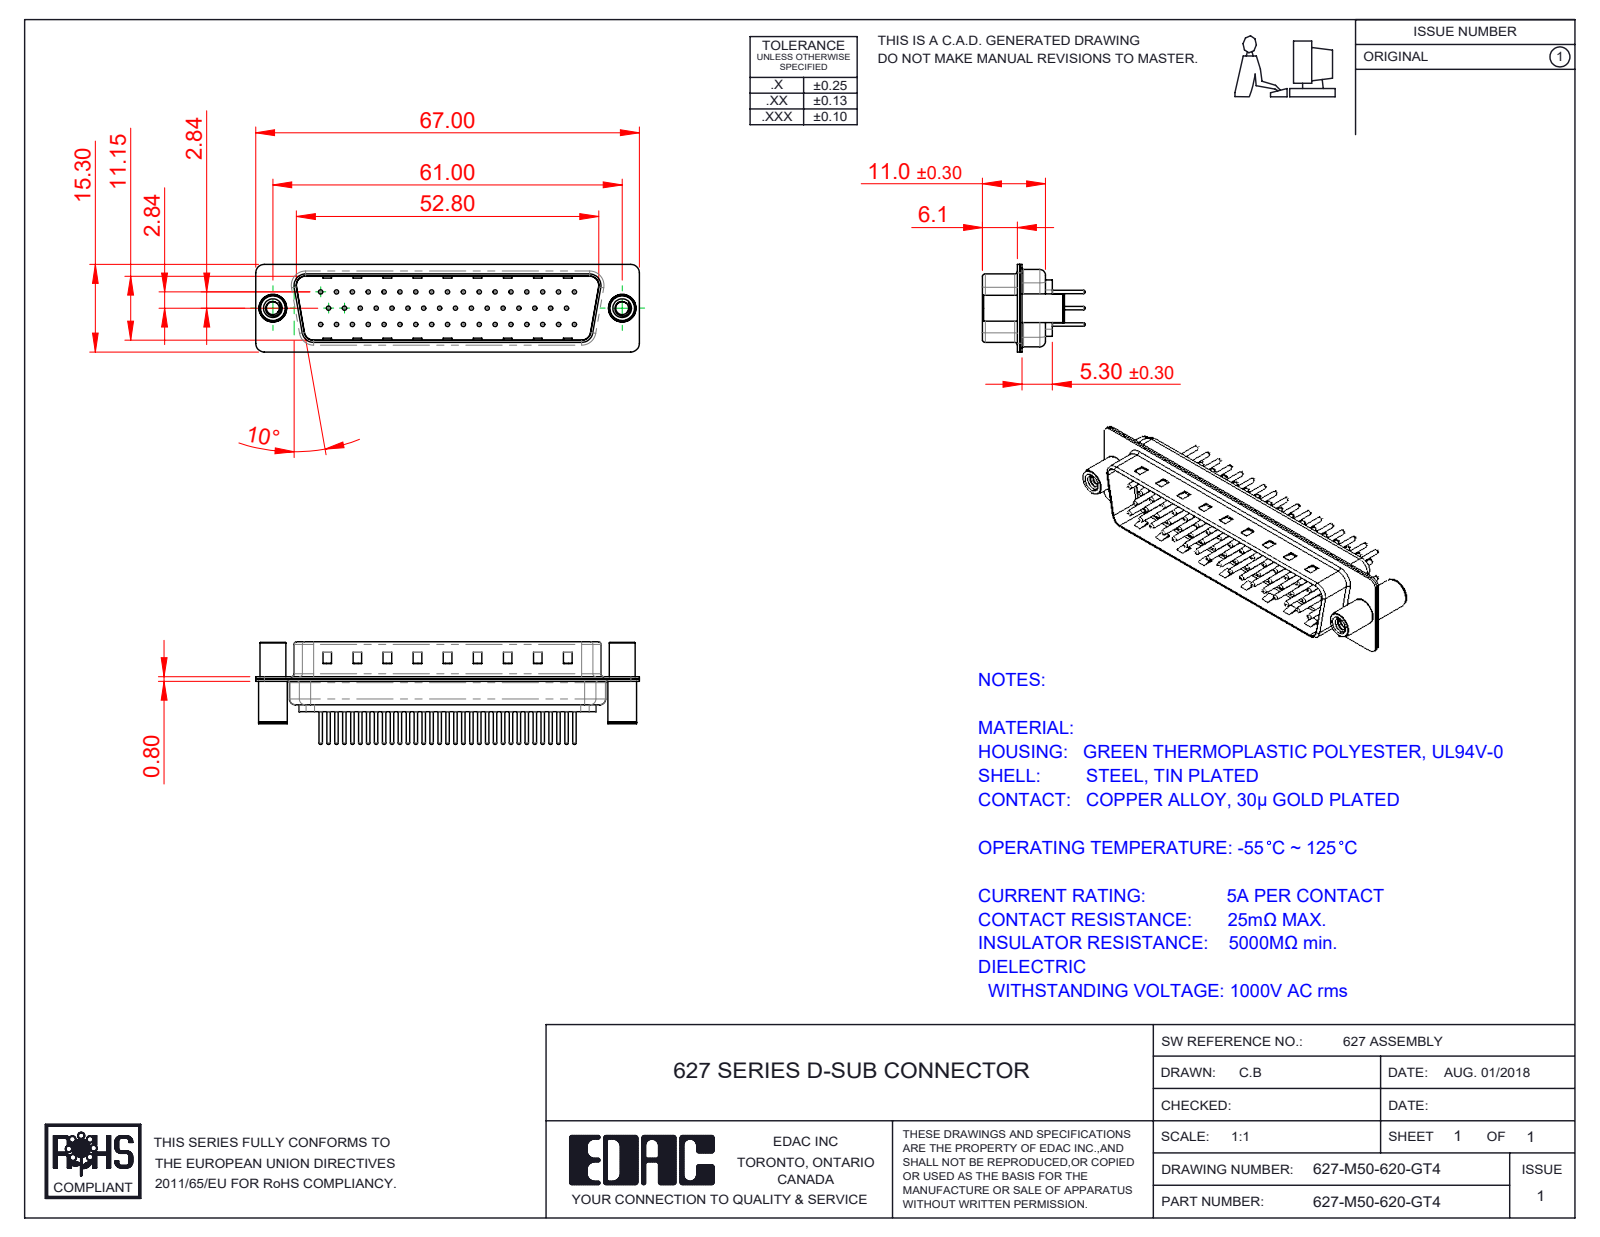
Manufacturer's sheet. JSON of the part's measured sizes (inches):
{"part_name": "627M Contact Row 1_20; 627M Contact Row 2_20; 627M Shell Front_50 Contacts; 627-M50-620-GT4 (+4 more)", "step_written_by": "SolidWorks 2020 (CONFIG_CONTROL_DESIGN)", "units": "inches", "bodies": {"solids": 55, "faces": 2348, "planar": 559, "cylindrical": 893, "other": 896}, "overall_size": [2.638, 0.705, 0.602], "volume_in3": 0.294, "surface_area_in2": 17.4, "round_holes": [[0.03, 50], [0.063, 50], [0.079, 50], [0.089, 2], [0.128, 2], [0.157, 2], [0.189, 2]], "round_bosses_or_shafts": [[0.059, 50], [0.024, 50], [0.197, 2], [0.193, 2], [0.177, 2]], "partial_cylinders_radius": [[0.059, 16], [0.079, 12], [0.02, 8], [0.063, 8], [0.01, 4], [0.024, 4], [0.026, 4], [0.035, 4]], "face_to_face_distances": [0.016, 0.455, 0.224, 0.24, 0.031, 0.03, 0.485, 0.209, 0.485, 0.516], "hole_center_spacings": [0.124, 0.109, 0.218, 0.327, 0.436, 0.545, 0.654, 0.198]}
